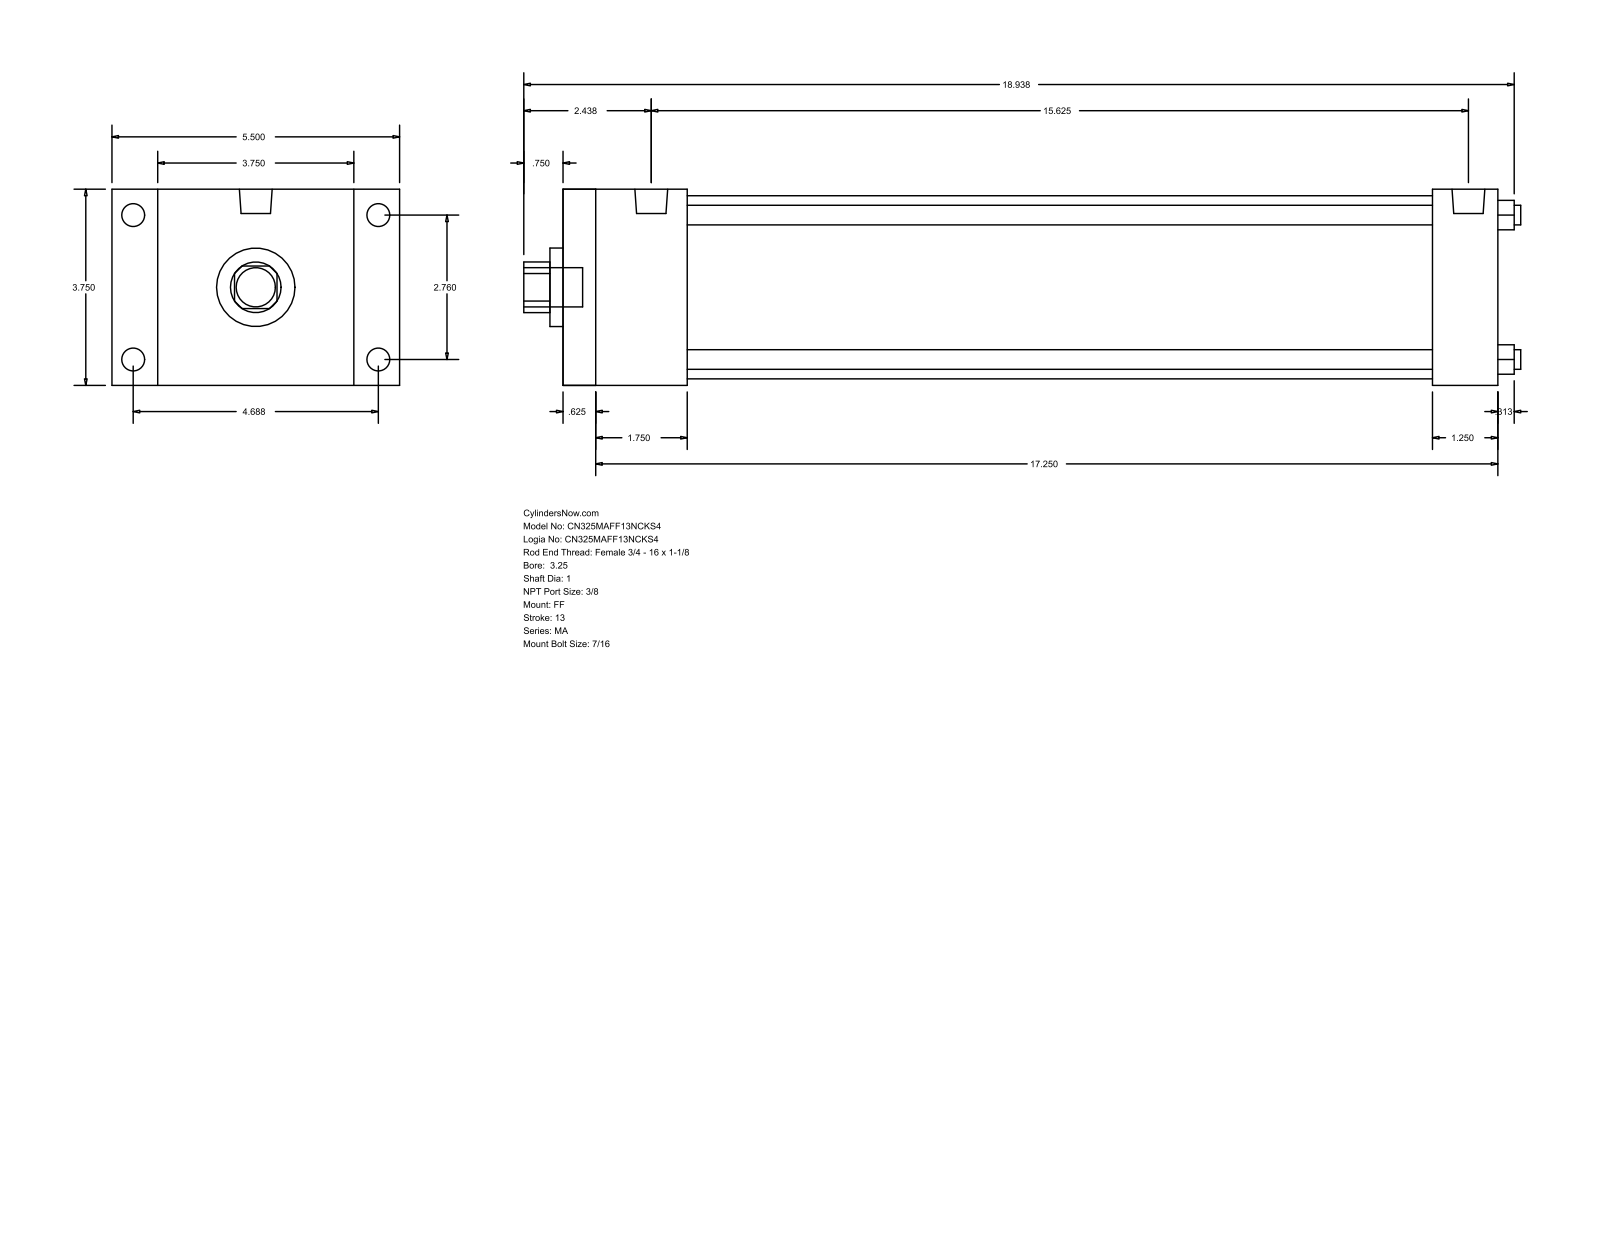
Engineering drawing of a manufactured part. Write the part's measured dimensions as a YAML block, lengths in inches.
part_name: "MA_FF__0325_1"
step_written_by: "GSSL Pune (CONFIG_CONTROL_DESIGN)"
units: inches
bodies: {solids: 0, faces: 92, planar: 64, cylindrical: 28, other: 0}
overall_size: [19.063, 5.5, 3.75]
round_holes:
  - {diameter: 0.375, count: 4}
  - {diameter: 1, count: 1}
  - {diameter: 1.5, count: 1}
  - {diameter: 3.5, count: 1}
round_bosses_or_shafts:
  - {diameter: 0.437, count: 8}
  - {diameter: 0.627, count: 2}
  - {diameter: 0.75, count: 1}
partial_cylinders:
  - {radius: 0.484, count: 1}
face_to_face_distances: [3.75, 17.875, 0.625, 17.25, 0.875, 4.625, 2.375, 16.625, 1.75, 16]
hole_center_spacings: [1.952, 2.76, 3.903]
